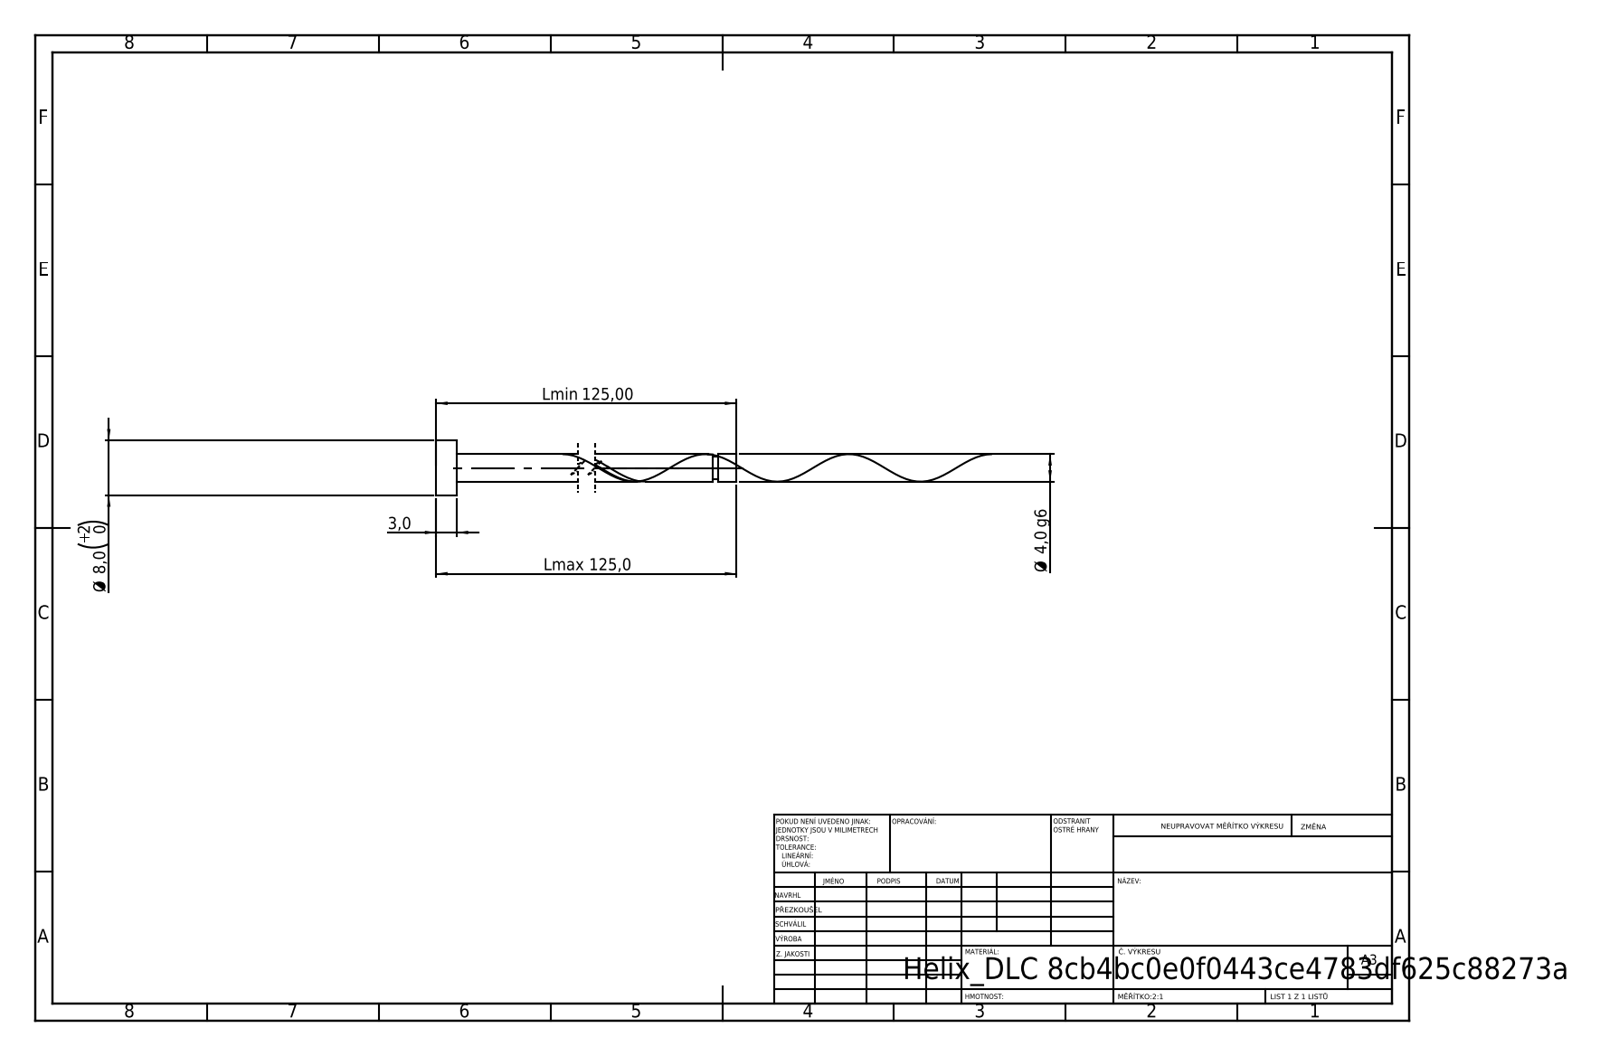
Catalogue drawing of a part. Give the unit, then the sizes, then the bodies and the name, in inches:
Units: inches
Overall size (bounding box): 4.921 × 0.315 × 0.315
Round bosses / shafts (diameter × count): ⌀0.315 ×1, ⌀0.157 ×1, ⌀0.126 ×1
Main face-to-face distances: 0.118, 4.921, 4.803, 4.817, 4.699, 0.104, 4.786, 4.668, 0.031, 0.135
Volume: 0.102 in³ · Surface area: 2.705 in²
Bodies: 1 solid, 21 faces (6 planar, 14 cylindrical, 1 other)
STEP written by: SolidWorks 2019 (CONFIG_CONTROL_DESIGN)
